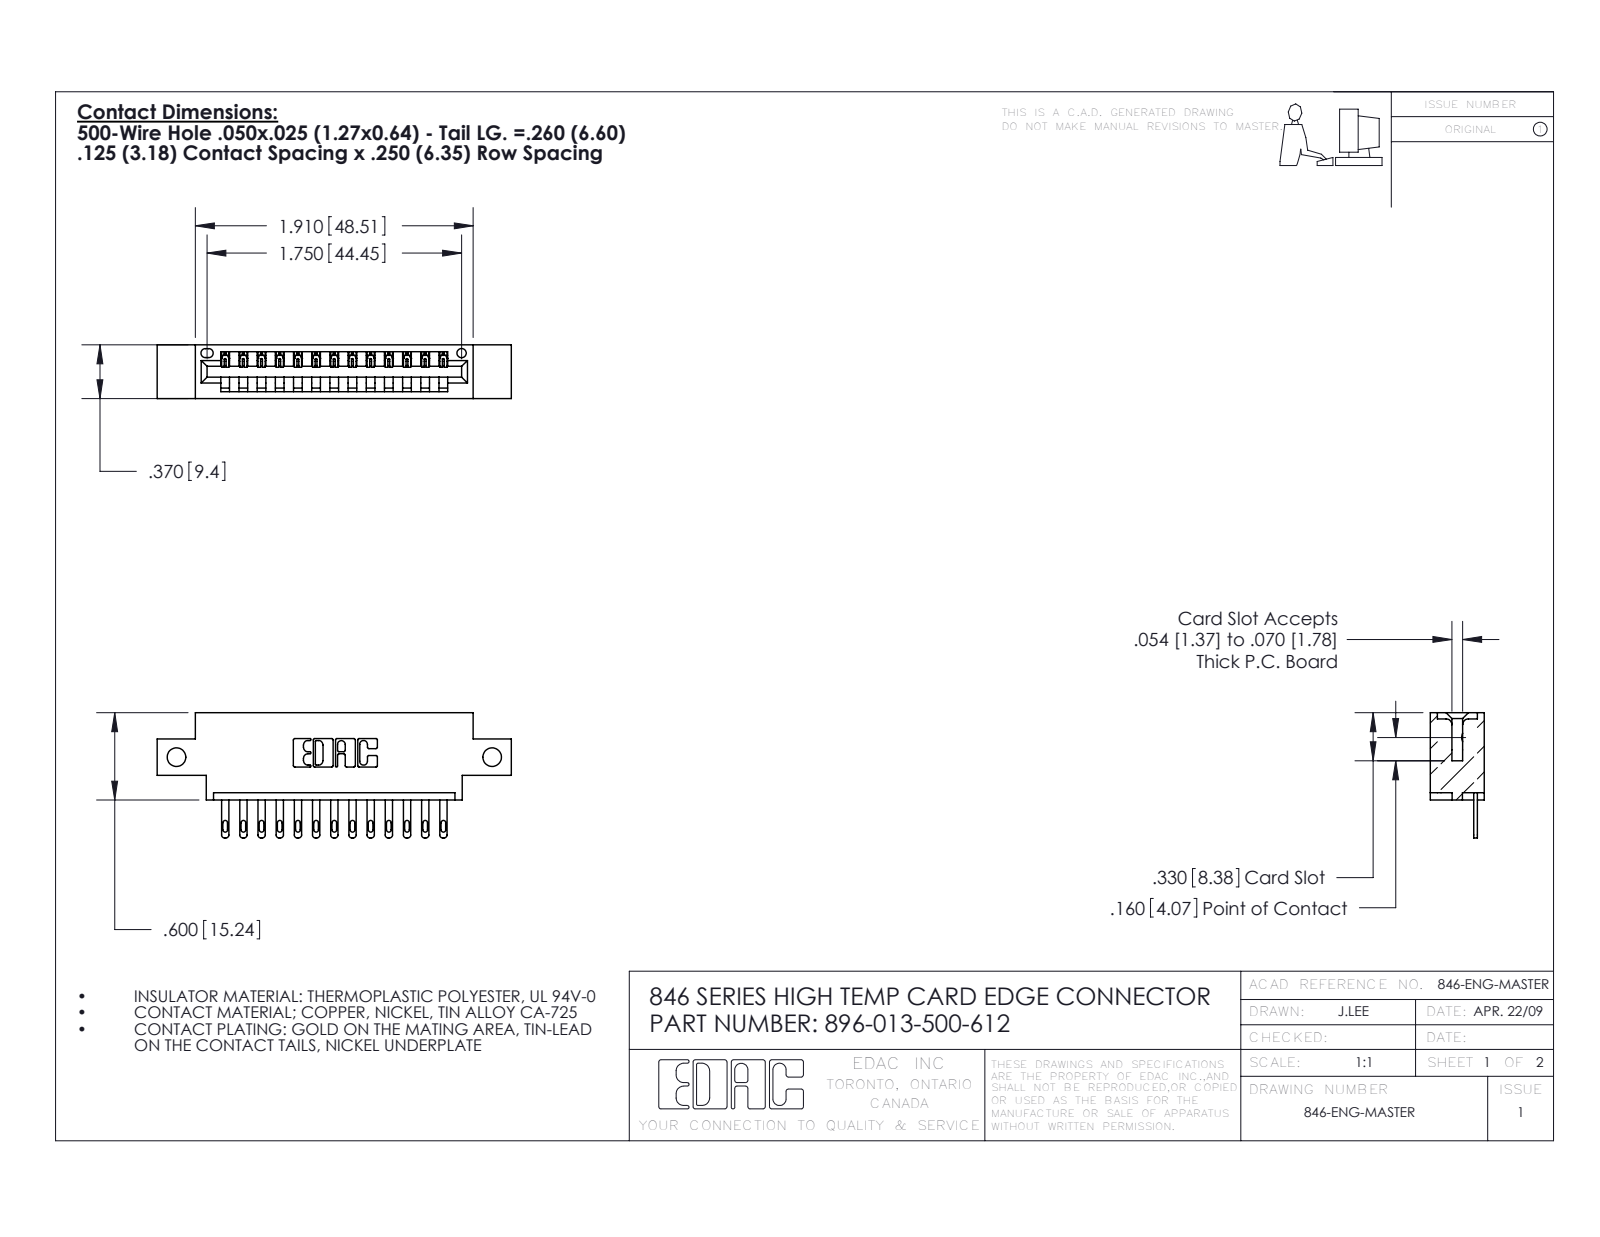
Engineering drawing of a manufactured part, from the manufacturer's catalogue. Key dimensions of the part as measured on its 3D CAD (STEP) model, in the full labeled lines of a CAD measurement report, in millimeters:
Part name (STEP PRODUCT): 896-013-500-612; 846 Part_0.170 Offset - Side Mount; 345-292-001_345-293-100
STEP written by: SolidWorks 2020 (CONFIG_CONTROL_DESIGN)
Units: millimetres
Bodies: 14 solids, 828 faces (522 planar, 306 cylindrical, 0 other)
Overall size (bounding box): 61.8 × 21.8 × 9.4
Volume: 5 490 mm³ · Surface area: 6 587 mm²
Round holes (diameter × count): ⌀3.3 ×2, ⌀1.6 ×1
Partial cylindrical surfaces — rounded edges, fillets, slot ends (radius × count): R0.2 ×26, R0.4 ×26, R0.5 ×26, R0.3 ×22, R0.2 ×6, R0.8 ×6, R0.7 ×3, R0.8 ×2
Main face-to-face distances: 6.4, 1.2, 8.2, 9.4, 1.8, 7.6, 0.6, 3.8, 5.6, 2.5
Hole centre spacings: 55.1
